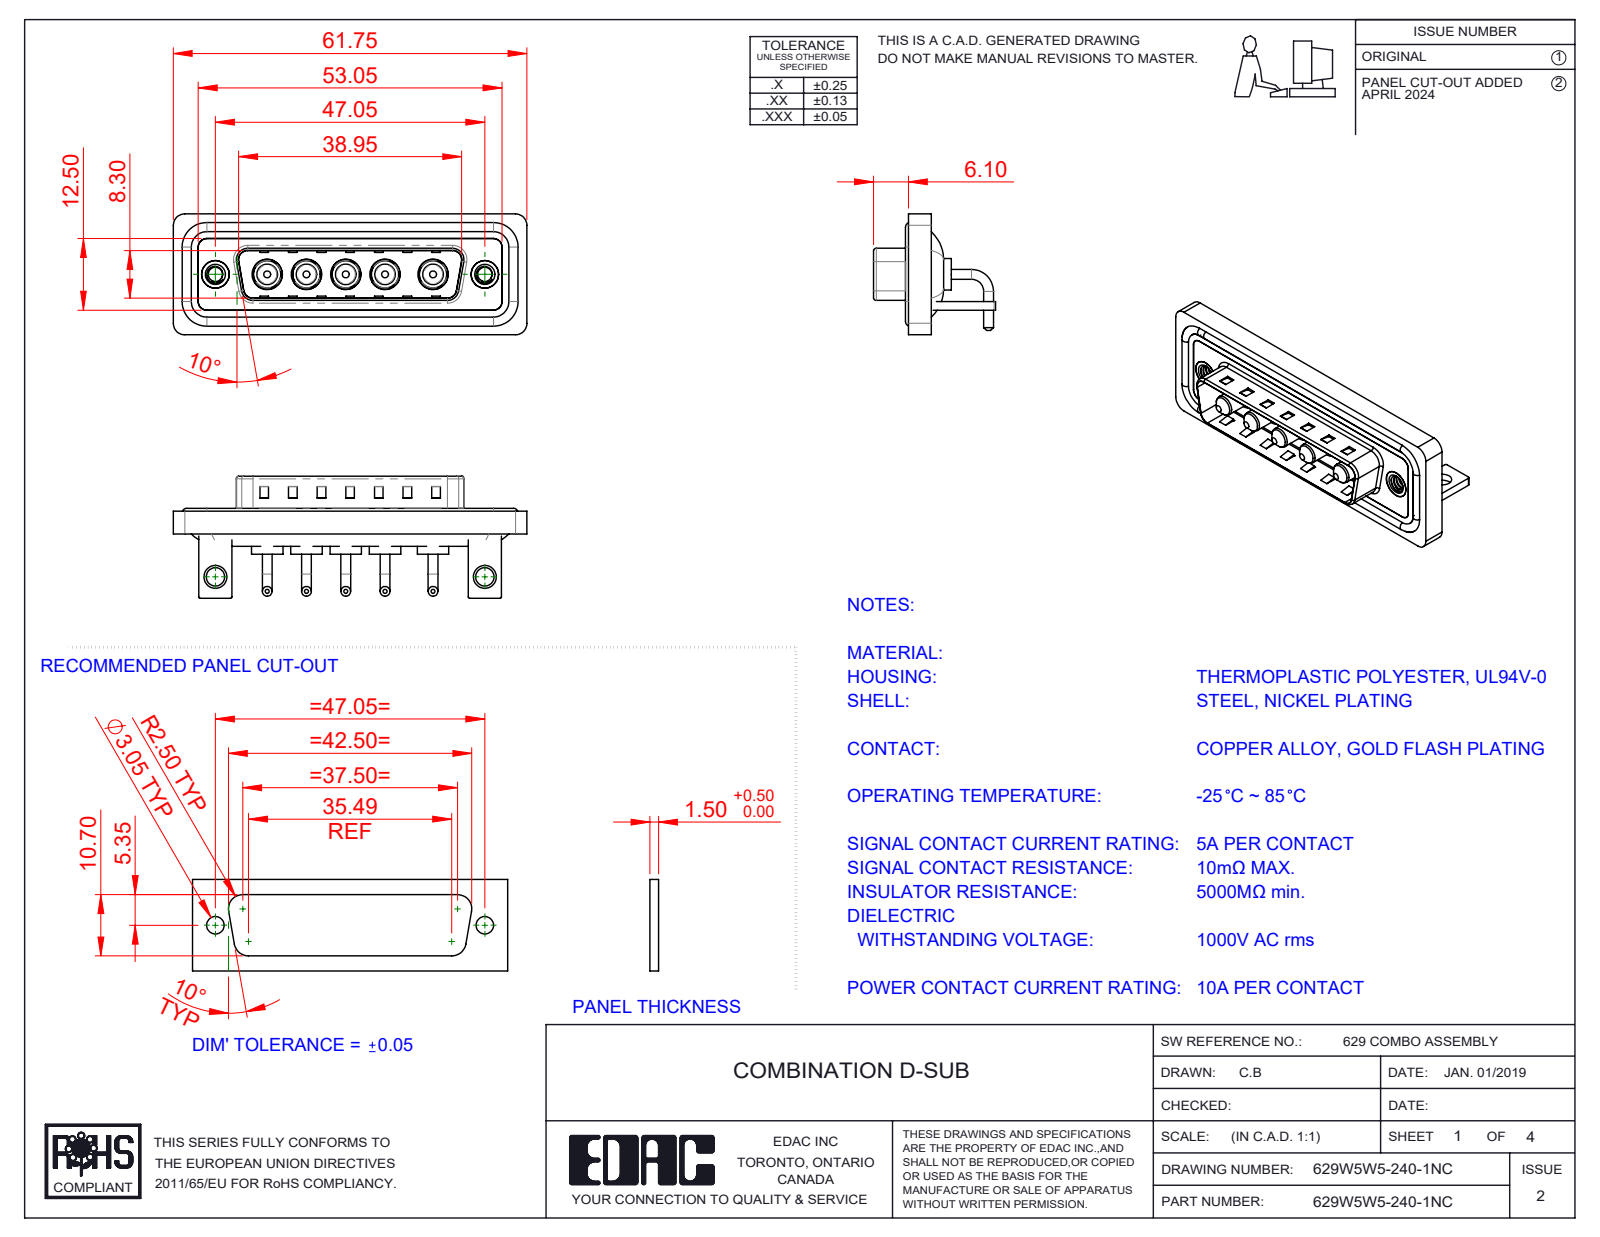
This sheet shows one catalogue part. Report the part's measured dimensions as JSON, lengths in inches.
{"part_name": "629W5W5-140-1NC; Power Pin_10A RA; 629Combo Housing_5W5; 629Combo Waterproof Housing_25 Contacts (+4 more)", "step_written_by": "SolidWorks 2023 (CONFIG_CONTROL_DESIGN)", "units": "inches", "bodies": {"solids": 19, "faces": 736, "planar": 279, "cylindrical": 311, "other": 146}, "overall_size": [2.431, 0.839, 0.831], "volume_in3": 0.475, "surface_area_in2": 19.54, "round_holes": [[0.191, 5], [0.209, 5], [0.098, 2], [0.126, 2], [0.157, 2], [0.189, 2], [0.197, 2]], "round_bosses_or_shafts": [[0.067, 10], [0.217, 5], [0.205, 5], [0.187, 5], [0.148, 5], [0.142, 5], [0.063, 4], [0.193, 2]], "partial_cylinders_radius": [[0.079, 19], [0.059, 18], [0.01, 16], [0.02, 9], [0.063, 8], [0.083, 5], [0.024, 4], [0.026, 4]], "face_to_face_distances": [0.016, 0.059, 0.114, 0.031, 0.083, 0.146, 0.043, 0.177, 0.161, 0.047], "hole_center_spacings": [0.27, 0.541, 1.852, 0.27, 0.27, 0.33, 0.33, 0.356]}
